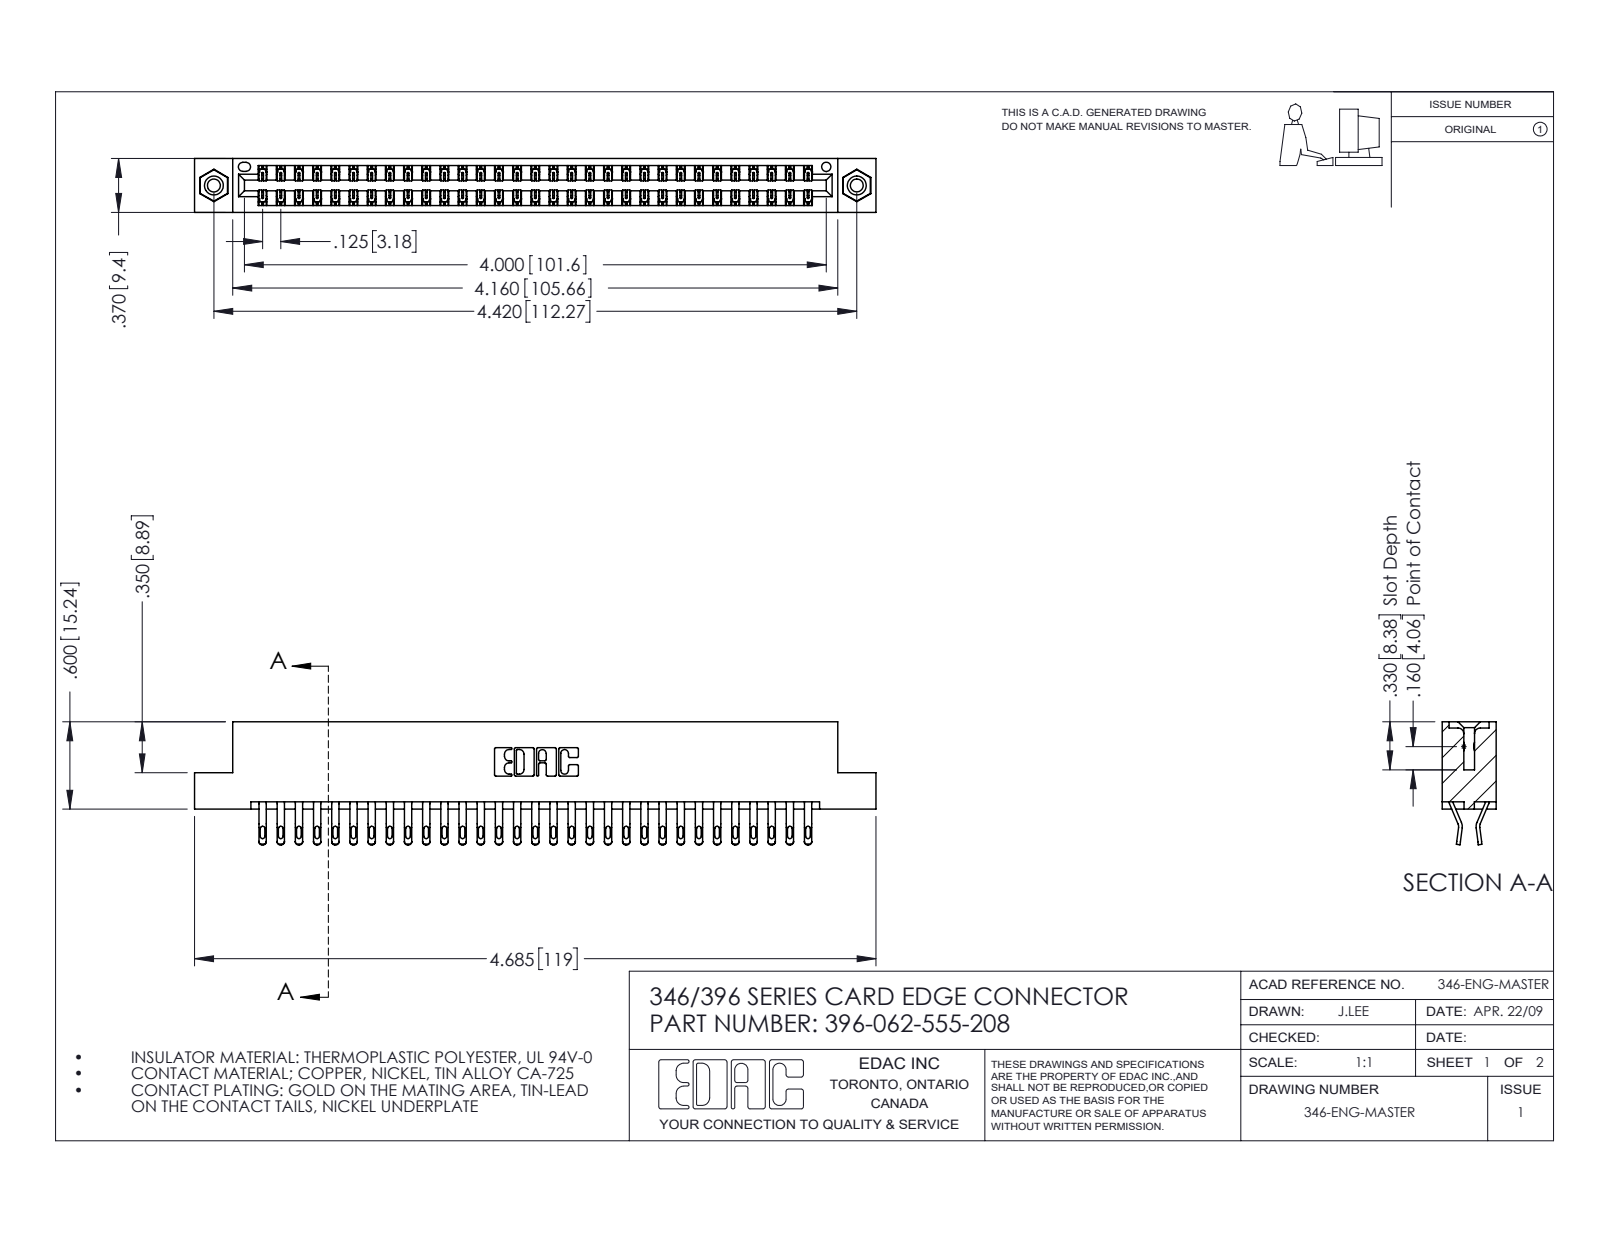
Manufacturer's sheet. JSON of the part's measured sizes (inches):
{"part_name": "346 Part_Flush Mounting Lugs - 0.156 Dia-TI; 396-062-555-208; 345-292-001_555 Tail; 345-250-001_345-250-003-102", "step_written_by": "SolidWorks 2016 (CONFIG_CONTROL_DESIGN)", "units": "inches", "bodies": {"solids": 65, "faces": 3778, "planar": 2154, "cylindrical": 1608, "other": 16}, "overall_size": [4.685, 0.845, 0.37], "volume_in3": 0.713, "surface_area_in2": 25.67, "round_holes": [[0.089, 2], [0.125, 2], [0.156, 2], [0.064, 1]], "round_bosses_or_shafts": [[0.155, 2]], "partial_cylinders_radius": [[0.016, 124], [0.02, 124], [0.006, 93], [0.01, 22], [0.007, 6], [0.031, 6], [0.026, 3], [0.01, 2]], "face_to_face_distances": [0.048, 0.322, 0.37, 0.25, 0.025, 0.072, 0.298, 0.275, 0.148, 0.222], "hole_center_spacings": [0.246, 4.212, 4.42]}
